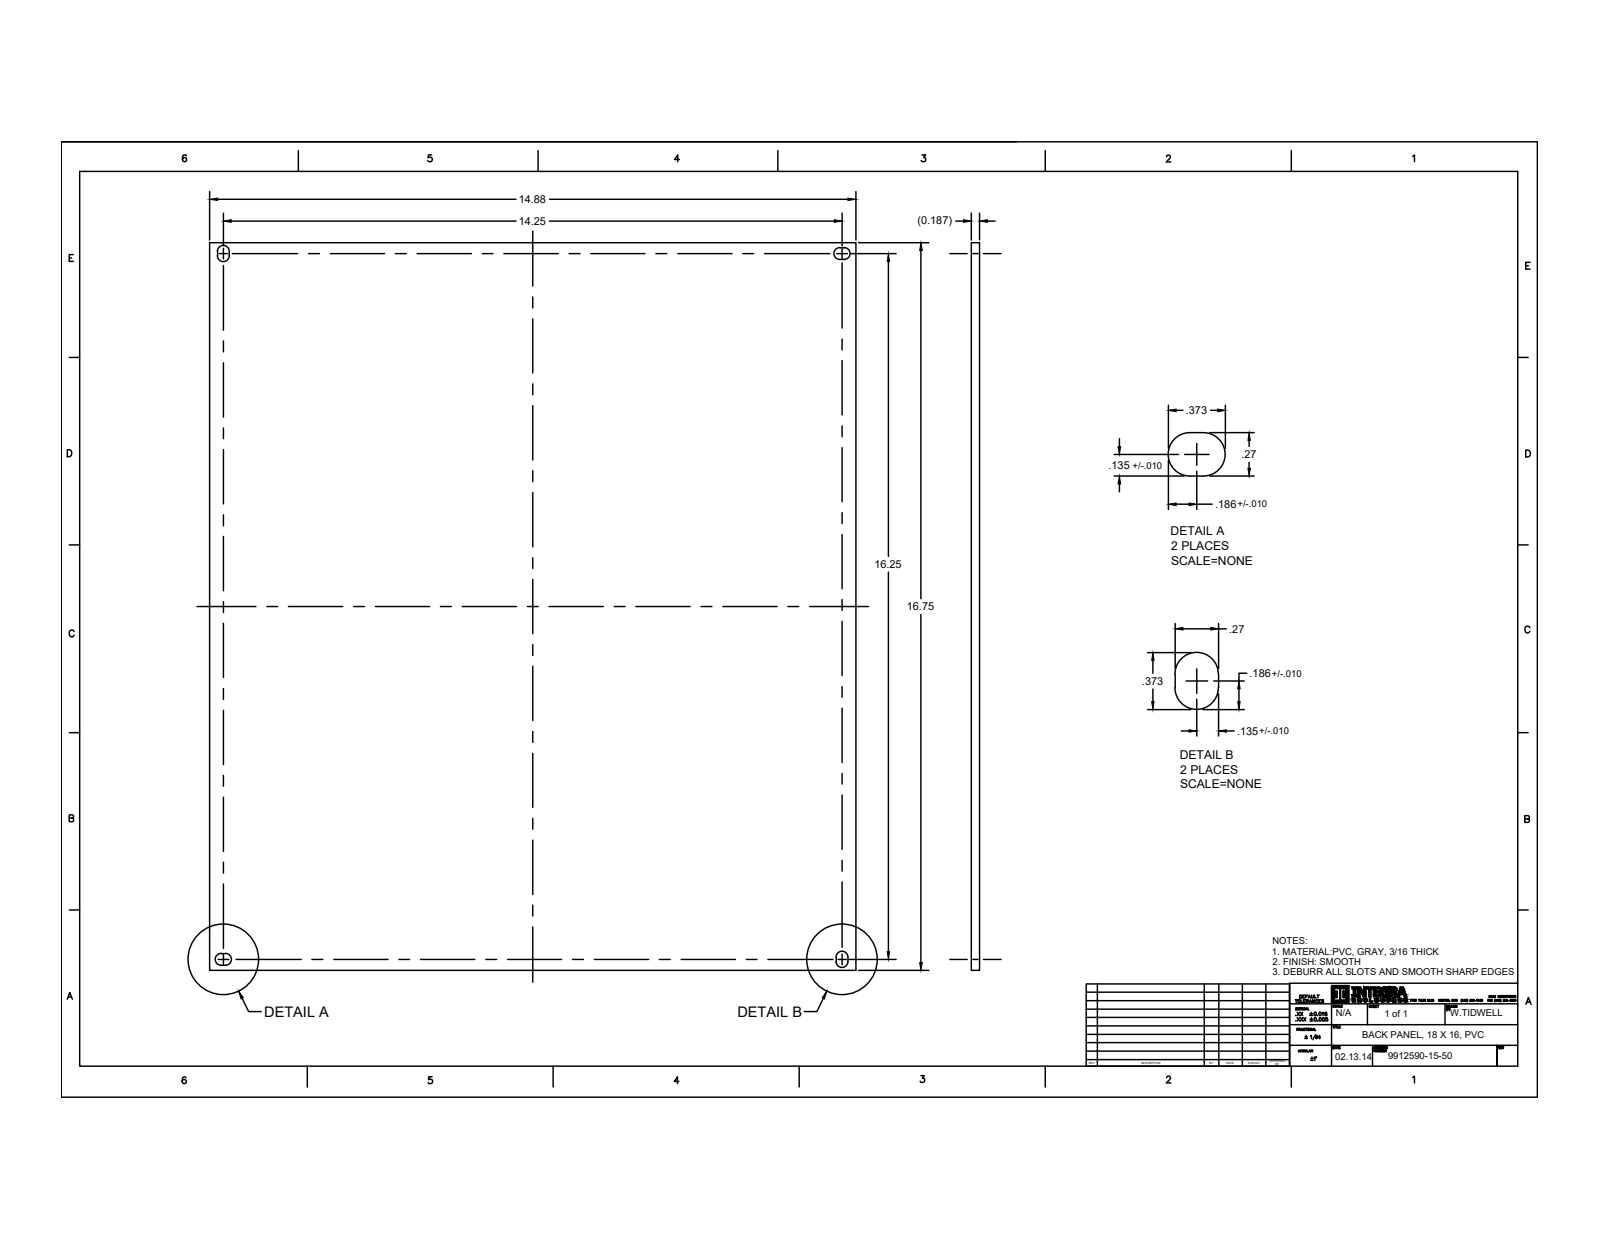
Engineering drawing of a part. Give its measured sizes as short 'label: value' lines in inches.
name: PVCBP-1816-P10
written by: SolidWorks 2018 (AUTOMOTIVE_DESIGN)
unit: in
bodies: 1 solid, 22 faces (14 planar, 8 cylindrical, 0 other)
size: 16.75 × 14.88 × 0.187
volume: 46.54 in³; area: 510.4 in²
rounds: 8× R0.135
face distances: 0.187, 14.88, 16.75, 0.27, 0.18, 0.45, 14.43, 14.7, 14.25, 16.25
